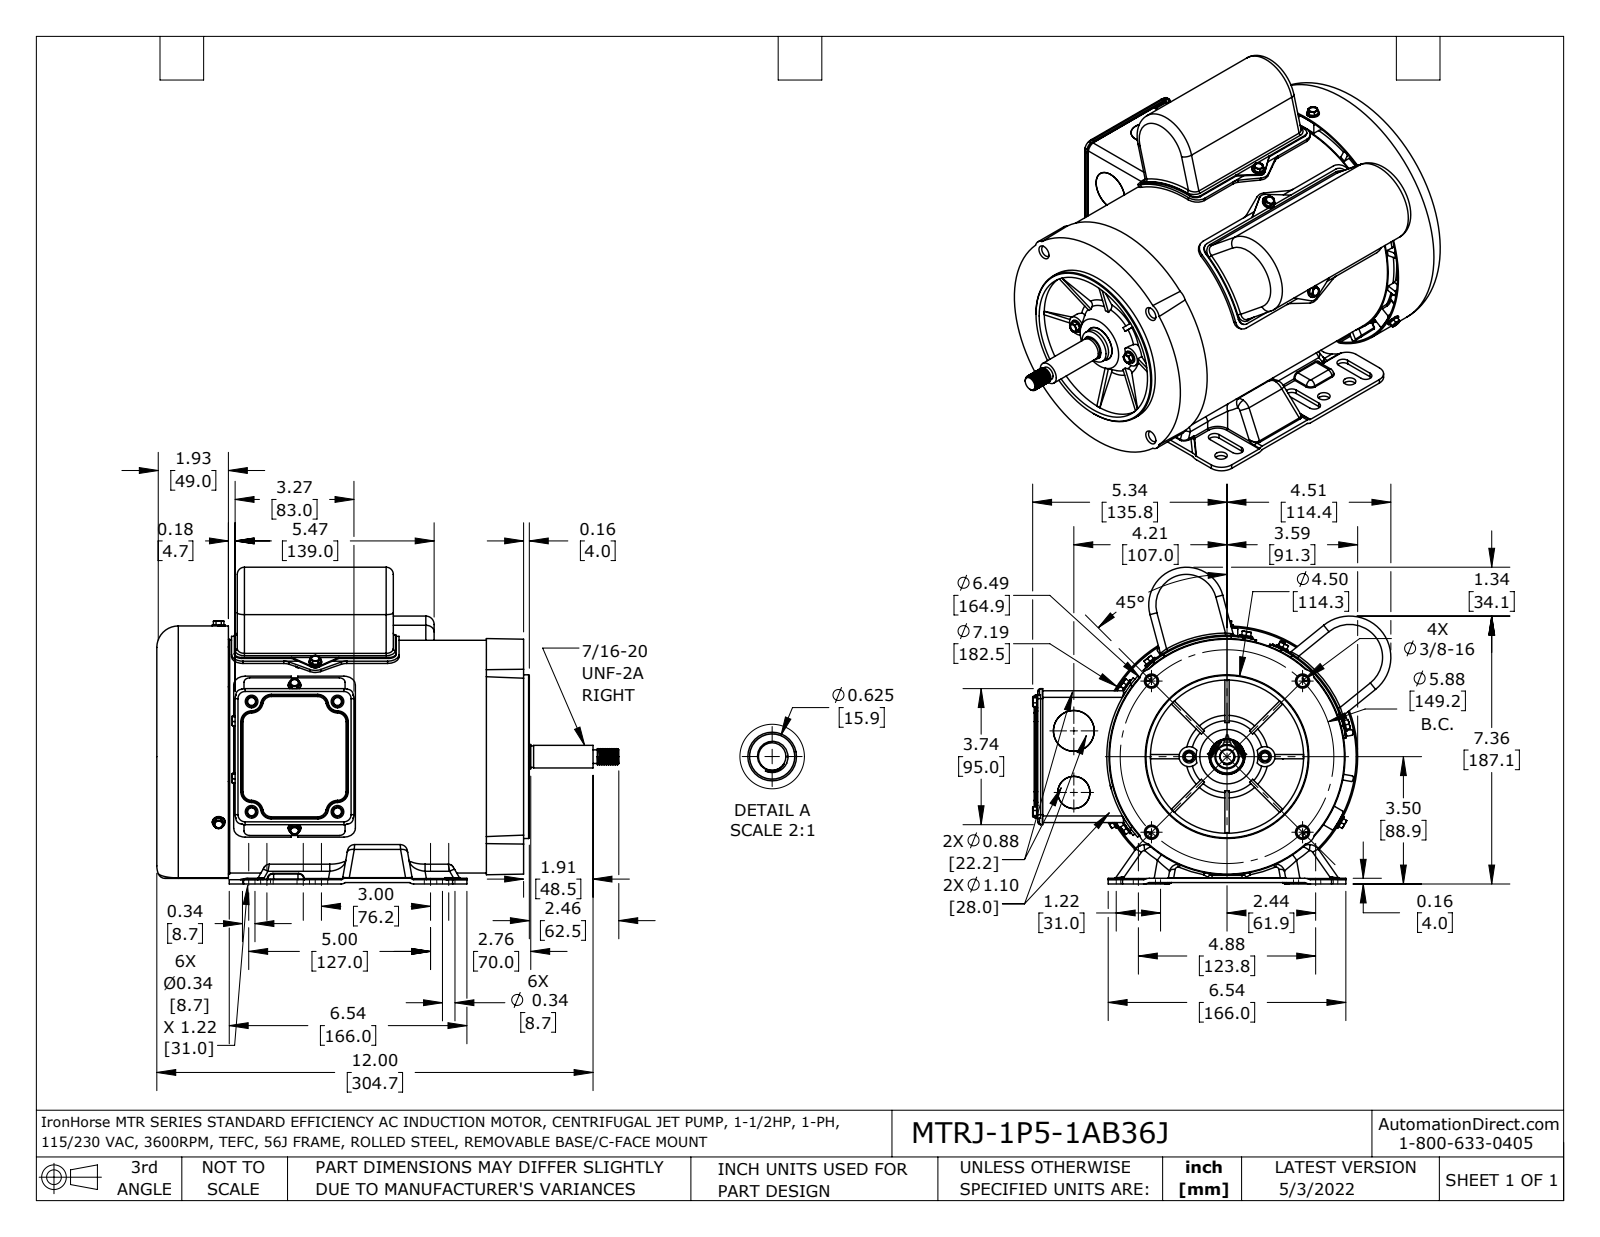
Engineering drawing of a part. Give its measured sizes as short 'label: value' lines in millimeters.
name: MTRJ-1P5-1AB36J redcmb1 coord
written by: SolidWorks 2021 (AUTOMOTIVE_DESIGN)
unit: mm
bodies: 36 solids, 3070 faces (761 planar, 1022 cylindrical, 1287 other)
size: 324.5 × 250.2 × 221.2
volume: 850 500 mm³; area: 734 200 mm²
holes: 17× ⌀5.6, 12× ⌀5, 9× ⌀3.5, 8× ⌀7, 6× ⌀4.5, 6× ⌀5.5, 6× ⌀8.7, 4× ⌀3.8, 4× ⌀8, 4× ⌀8.3, 4× ⌀18, 2× ⌀3.4
bosses: 17× ⌀4.2, 13× ⌀8.8, 4× ⌀8.8, 4× ⌀6, 1× ⌀182.5, 1× ⌀162.5, 1× ⌀114.3, 1× ⌀24
rounds: 117× R3, 57× R1, 32× R4, 30× R0.5, 26× R3.5, 24× R5, 20× R5.8, 18× R2
face distances: 0.8, 1, 3, 1.6, 270, 269, 4, 90.4, 78.4, 2
hole spacings: 107.2, 77, 2.4, 58.9, 61.2, 74.6, 95.2, 97.6
